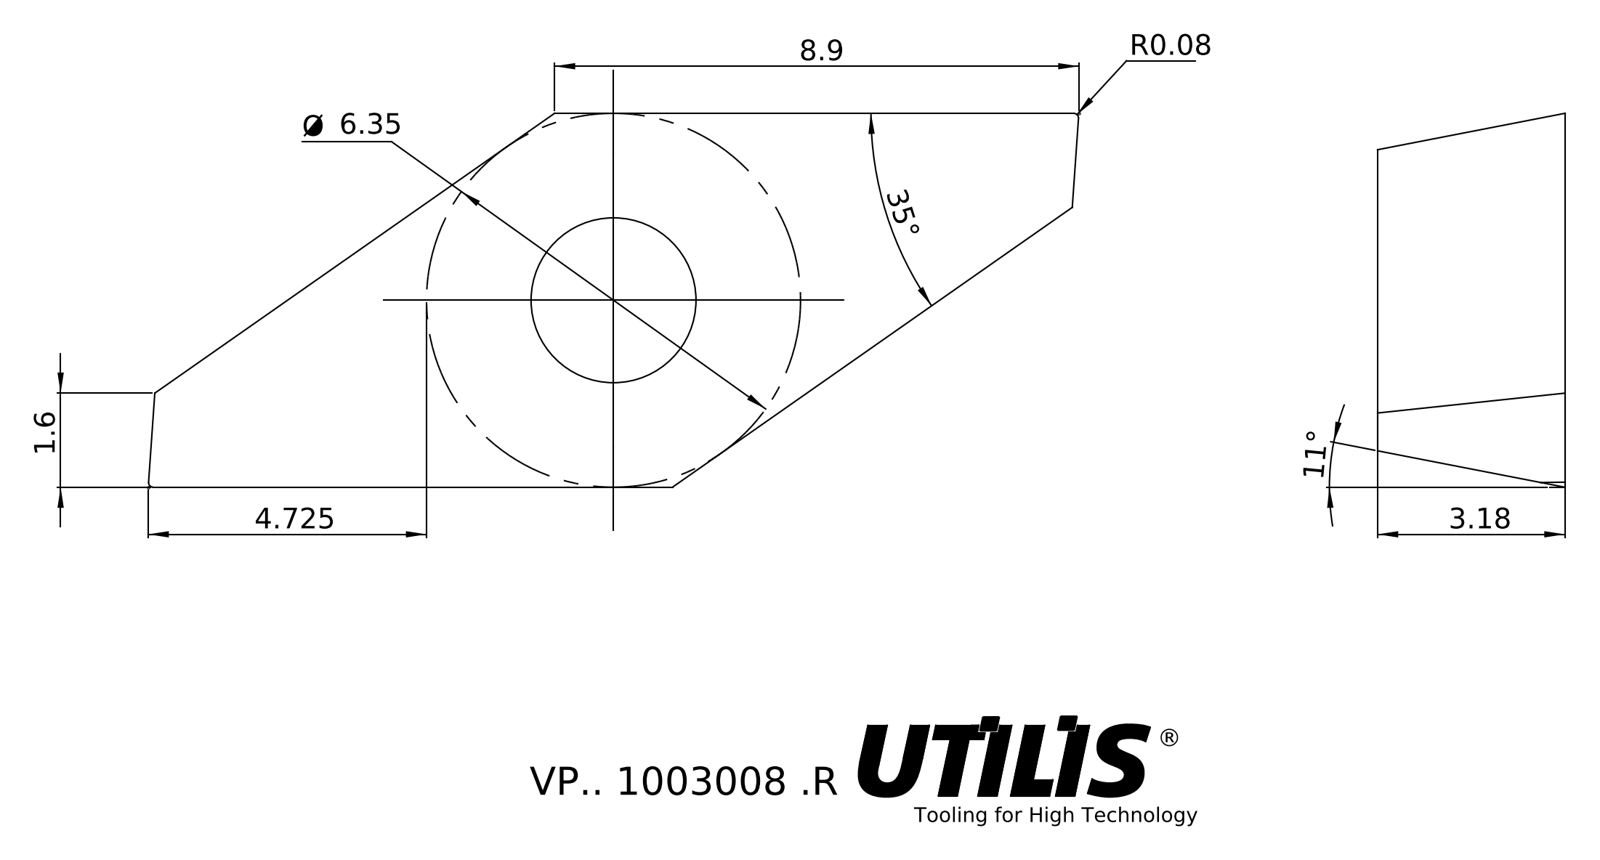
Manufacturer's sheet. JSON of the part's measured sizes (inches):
{"part_name": "VP.. 1003008 .R", "step_written_by": "SolidWorks 2016 (AUTOMOTIVE_DESIGN)", "units": "inches", "bodies": {"solids": 1, "faces": 13, "planar": 8, "cylindrical": 2, "other": 3}, "overall_size": [0.622, 0.25, 0.125], "volume_in3": 0.01, "surface_area_in2": 0.375, "round_holes": [[0.11, 1]], "face_to_face_distances": [0.125]}
